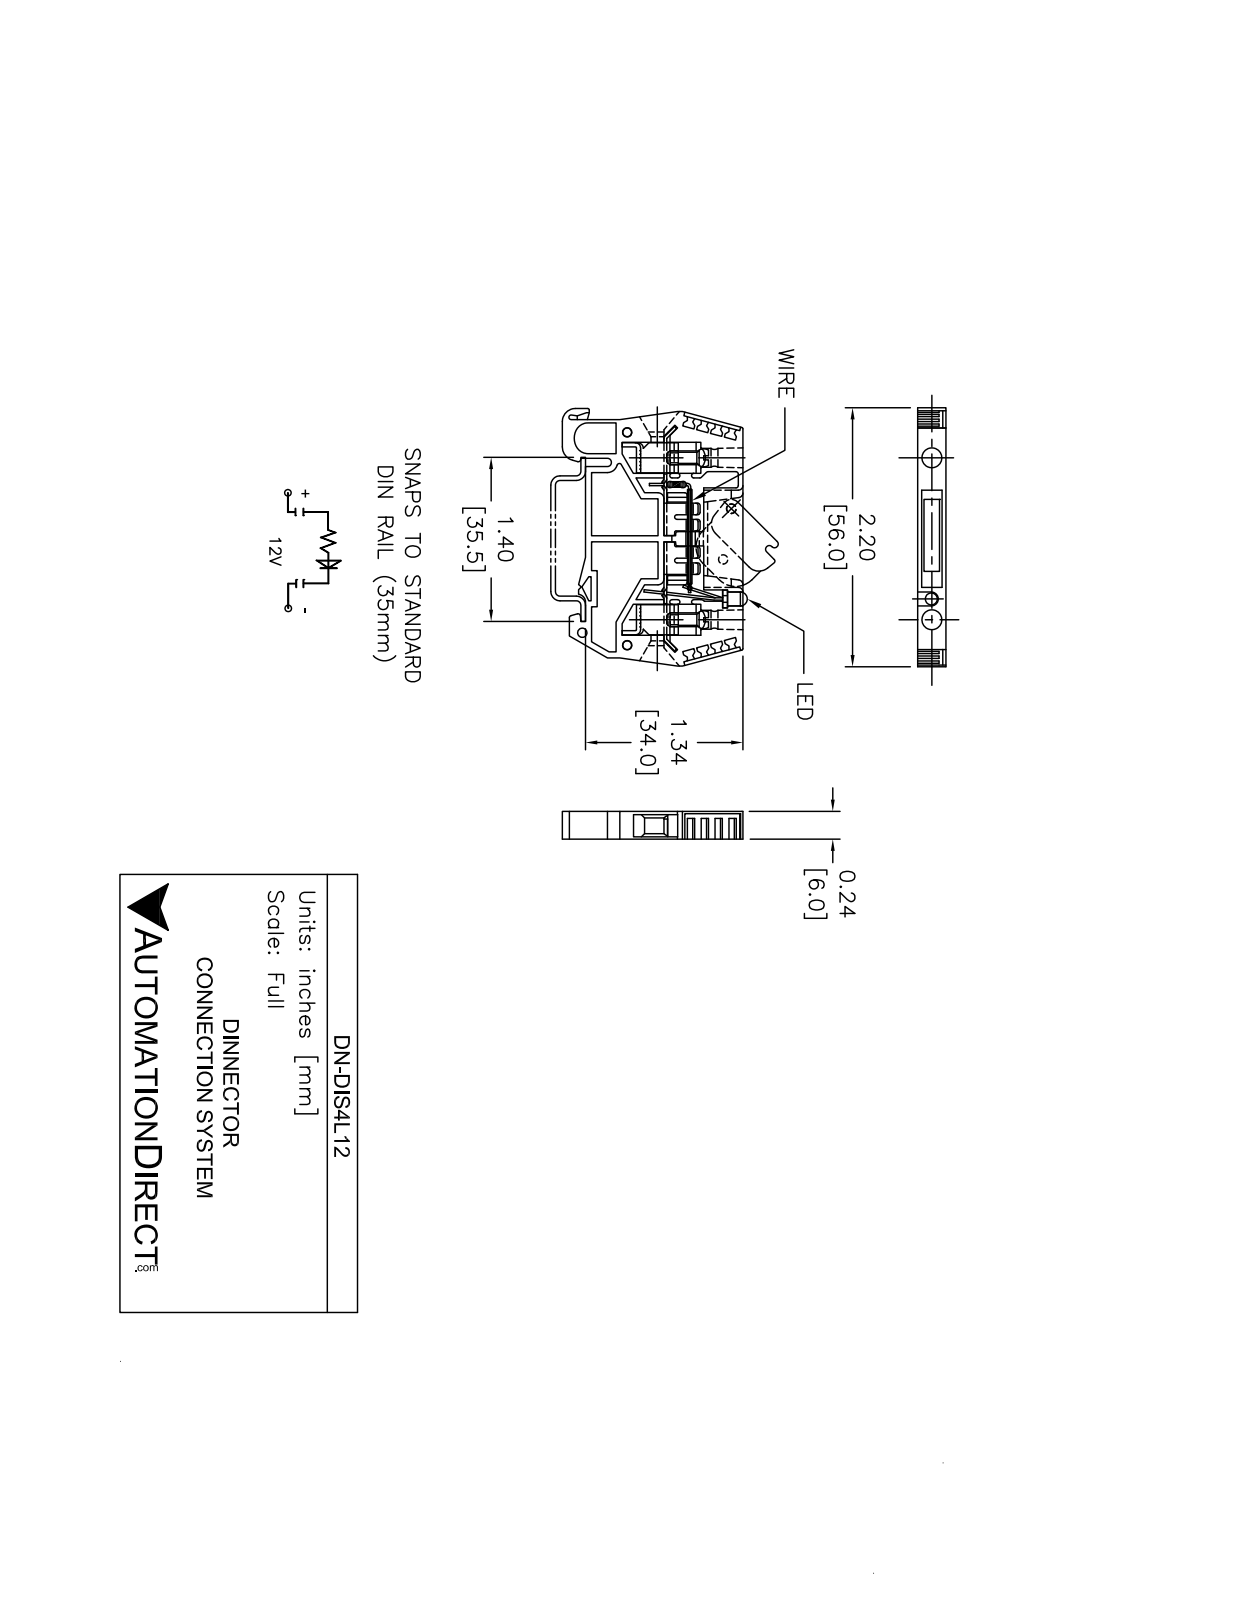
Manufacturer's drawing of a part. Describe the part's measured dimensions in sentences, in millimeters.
The part is named "4358104_DN-DIS4L12; 435K0001; 4258100_DN-QFE4; 20621_1". Its 3-D file was written by "SolidWorks 2013 (AUTOMOTIVE_DESIGN)". It is 3 solids with 425 faces: 250 planar, 117 cylindrical and 58 other. Overall it measures 55.65 by 39.6 by 6 millimeters. Its volume is 9 476 cubic millimeters and its surface area 7 242 square millimeters. Round holes: 4 of diameter 2, 2 of diameter 4.1. Round bosses or shafts: 10 of diameter 0.3, 1 of diameter 4, 1 of diameter 3, 1 of diameter 2. Partial cylindrical surfaces (rounded edges, fillets, slot ends): 24 of radius 0.5, 7 of radius 3, 3 of radius 1, 2 of radius 0.8, 2 of radius 1.3, 2 of radius 5, 1 of radius 0.9, 1 of radius 1.05. The main face-to-face distances are 6, 0.5, 3.5, 2, 2.5, 2.75, 5.5, 34, 0.6, 2.2. The hole center spacings are 10.07, 26.45, 26.89, 30.67, 35, 44.38, 46.
